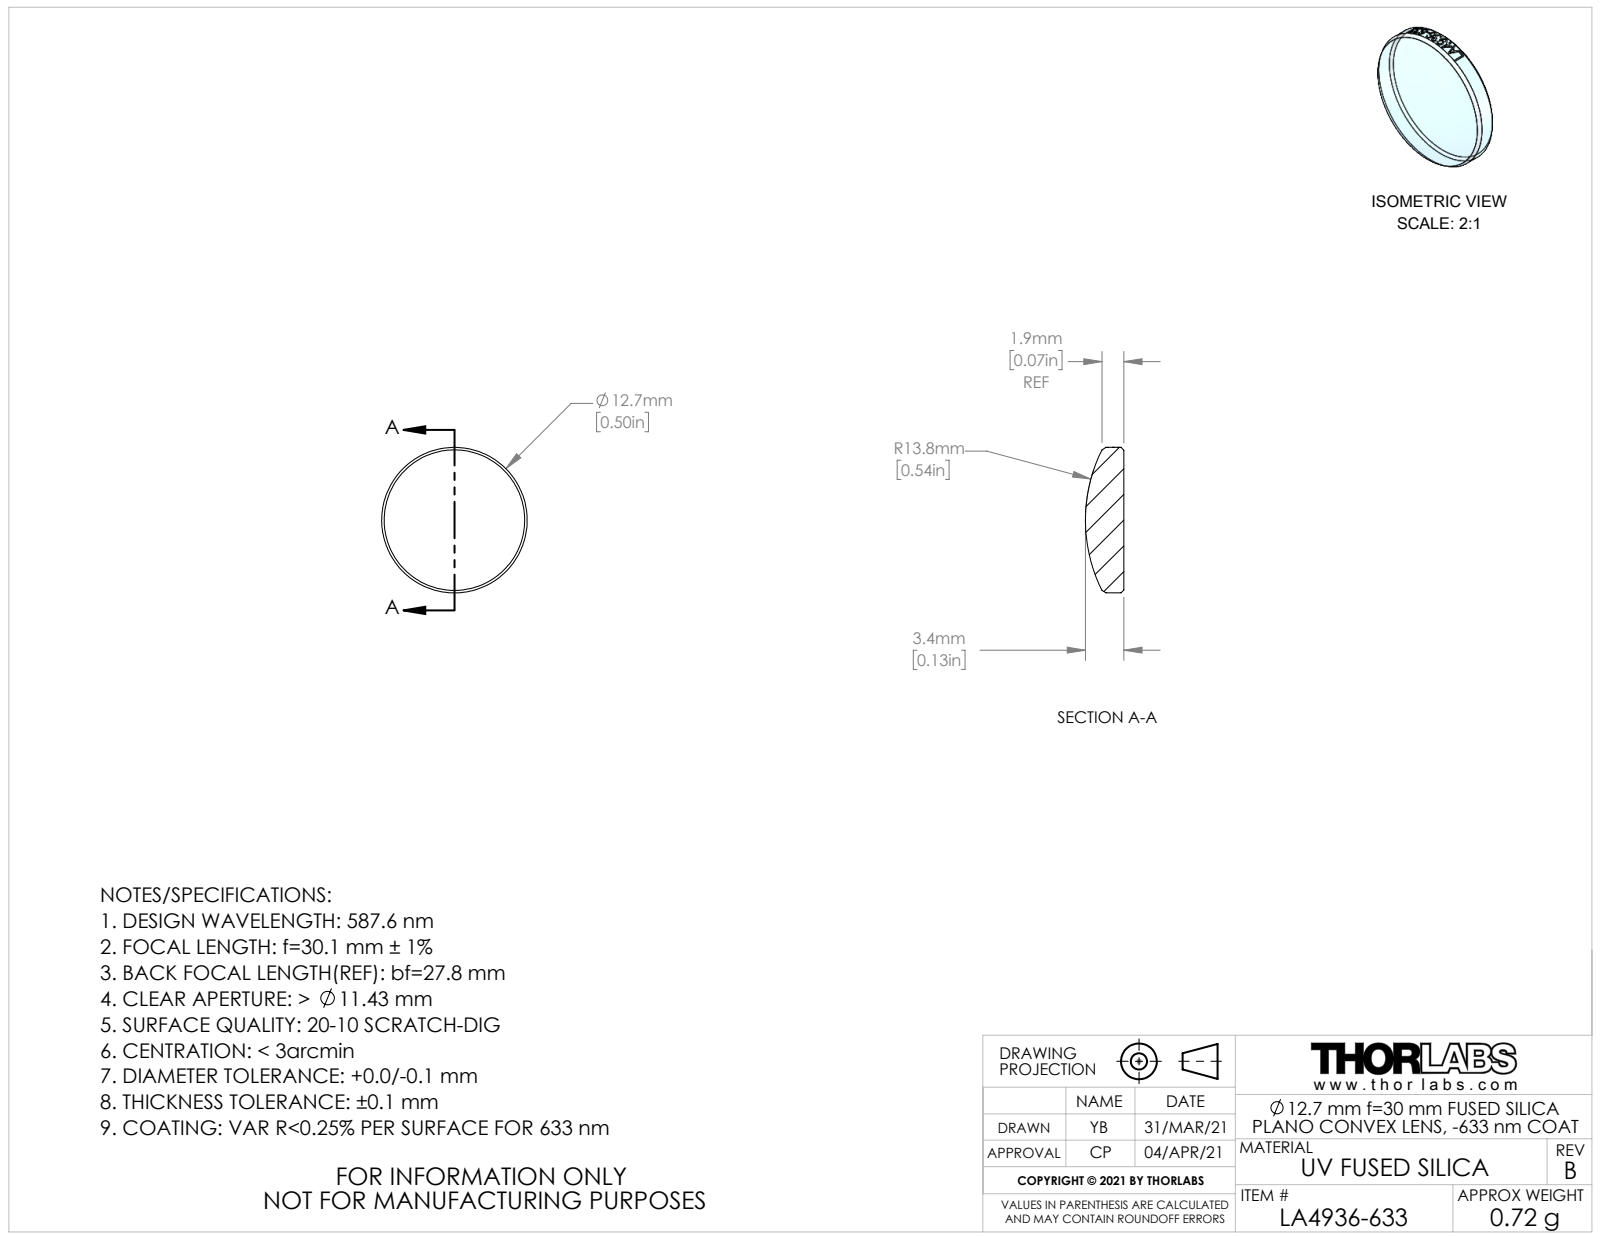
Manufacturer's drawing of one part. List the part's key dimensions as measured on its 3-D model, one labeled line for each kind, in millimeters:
Part name (STEP PRODUCT): CTN015002; CTN014982-999
STEP written by: SolidWorks 2018 (AUTOMOTIVE_DESIGN)
Units: millimetres
Bodies: 1 solid, 24 faces (1 planar, 17 cylindrical, 6 other)
Overall size (bounding box): 12.7 × 12.7 × 3.34
Volume: 325 mm³ · Surface area: 323 mm²
Round bosses / shafts (diameter × count): ⌀12.7 ×1
